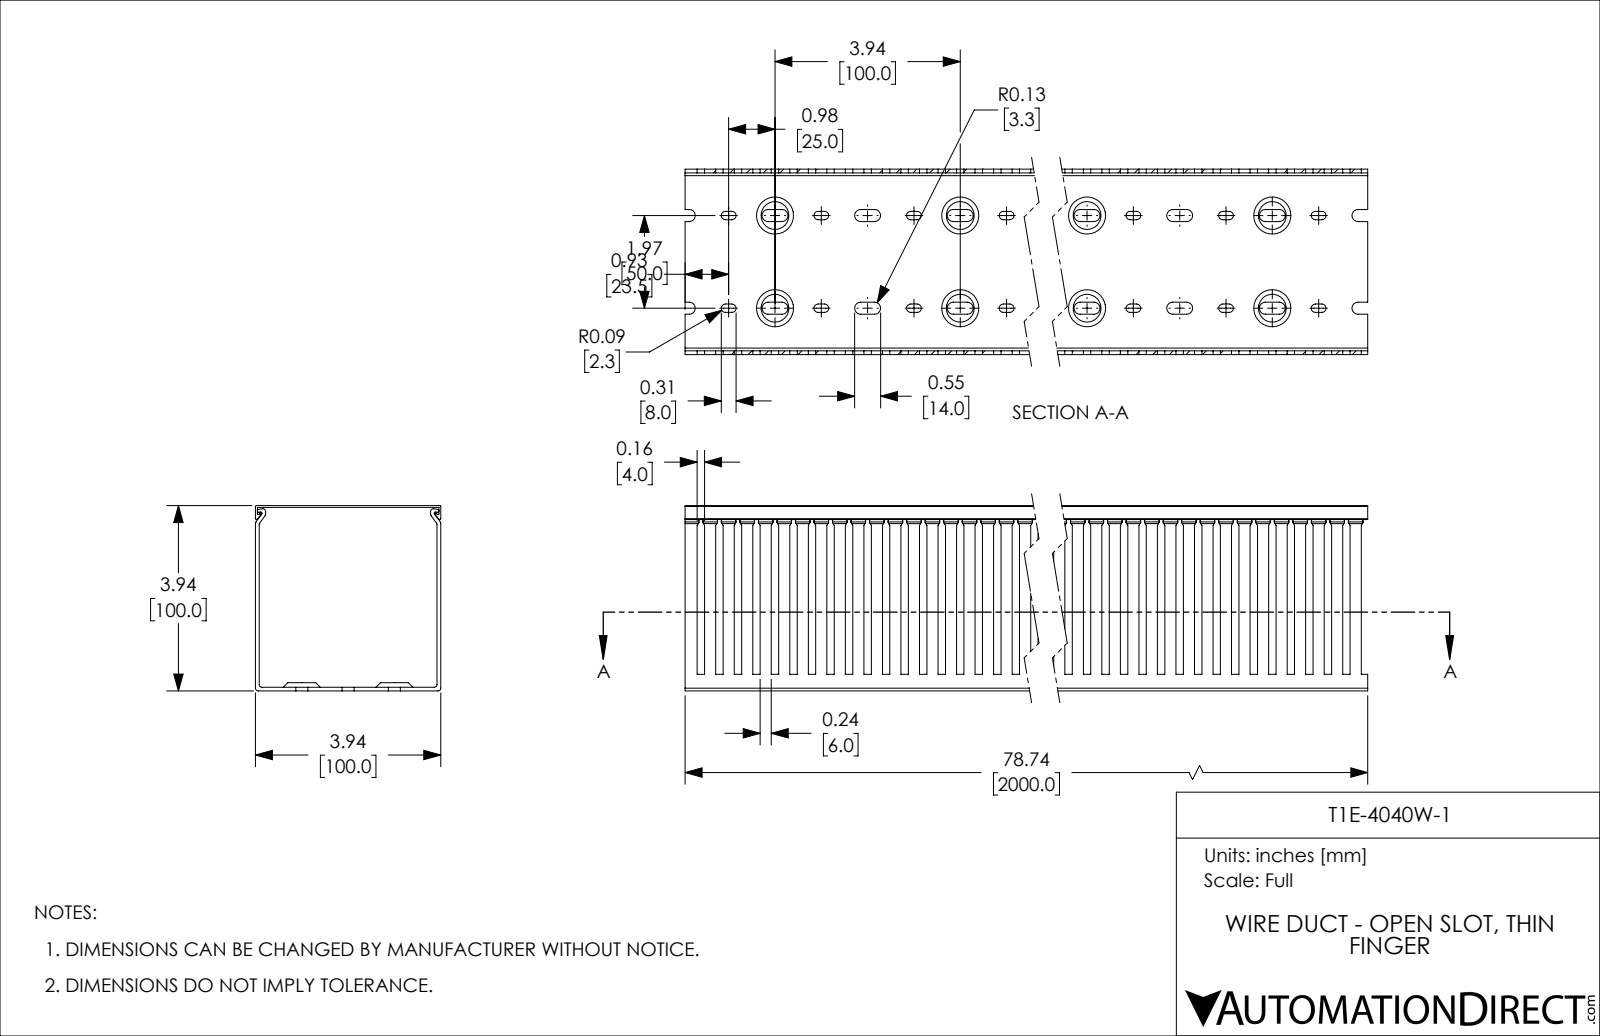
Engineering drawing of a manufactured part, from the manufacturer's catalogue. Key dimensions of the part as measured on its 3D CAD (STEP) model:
Part name (STEP PRODUCT): T1E-4040W-1
STEP written by: SolidWorks 2021 (CONFIG_CONTROL_DESIGN)
Units: millimetres
Bodies: 2 solids, 1573 faces (762 planar, 731 cylindrical, 80 other)
Overall size (bounding box): 2000 × 100 × 100
Volume: 1 411 000 mm³ · Surface area: 1 652 000 mm²
Partial cylindrical surfaces — rounded edges, fillets, slot ends (radius × count): R3.25 ×200, R2.25 ×160, R1.5 ×12, R0.5 ×8, R0.75 ×6
Main face-to-face distances: 2, 98, 100, 1, 99, 97, 96, 4.5, 94.5, 5.5
